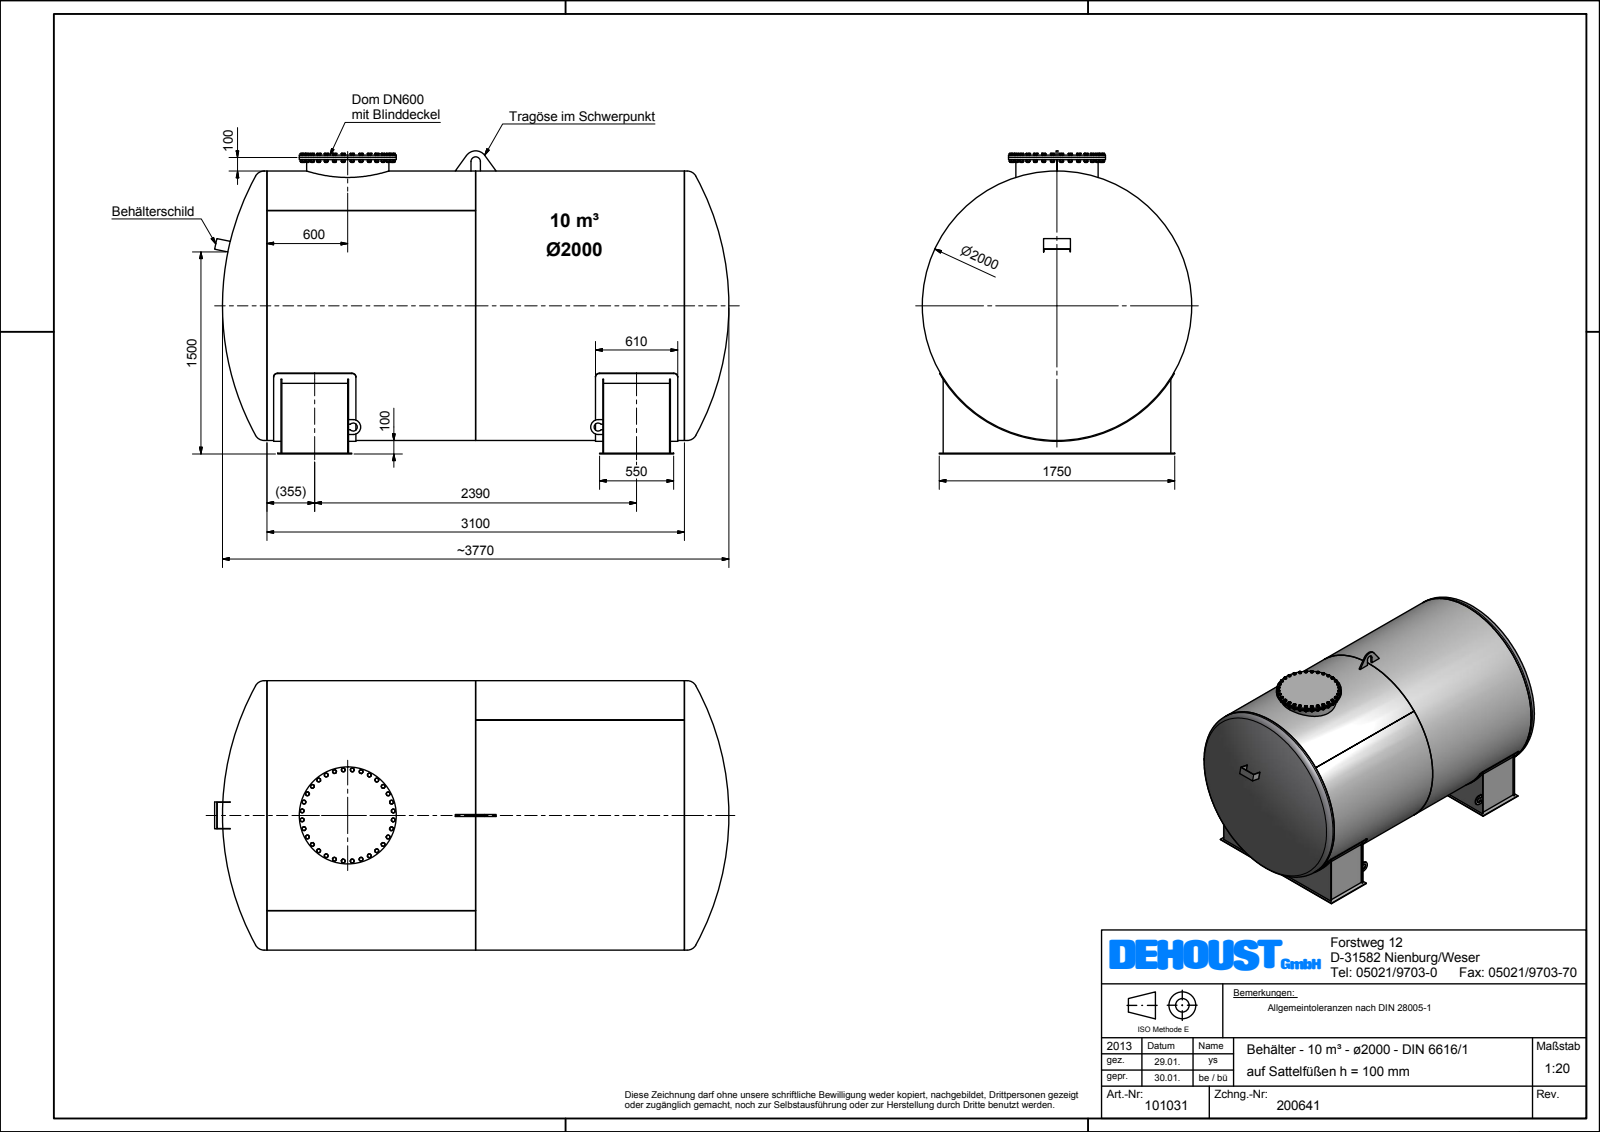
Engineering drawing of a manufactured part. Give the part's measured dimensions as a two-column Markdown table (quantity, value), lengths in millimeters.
| quantity | value |
| --- | --- |
| part name | Beh\\S\\dlter_6616_E_2000_010_100_KV |
| STEP written by | Autodesk Inventor 2012 (AUTOMOTIVE_DESIGN) |
| units | millimeters |
| bodies | 3 solids, 1109 faces (656 planar, 161 cylindrical, 292 other) |
| overall size | 3818.87 × 2250 × 2000 |
| volume | 1 429 000 000 mm³ |
| surface area | 63 110 000 mm² |
| round holes (diameter × count) | 598 × 1, 1988 × 1 |
| round bosses / shafts (diameter × count) | 24.8 × 32, 18 × 32, 16.65 × 32, 2000 × 1, 720 × 1, 660 × 1, 610 × 1 |
| partial cylindrical surfaces (radius × count) | 30 × 8, 29.73 × 2, 55 × 2, 35 × 1, 85 × 1, 1006 × 1 |
| main face-to-face distances | 6, 3100, 2390, 496, 1644, 104, 2996, 606, 2494, 502 |
